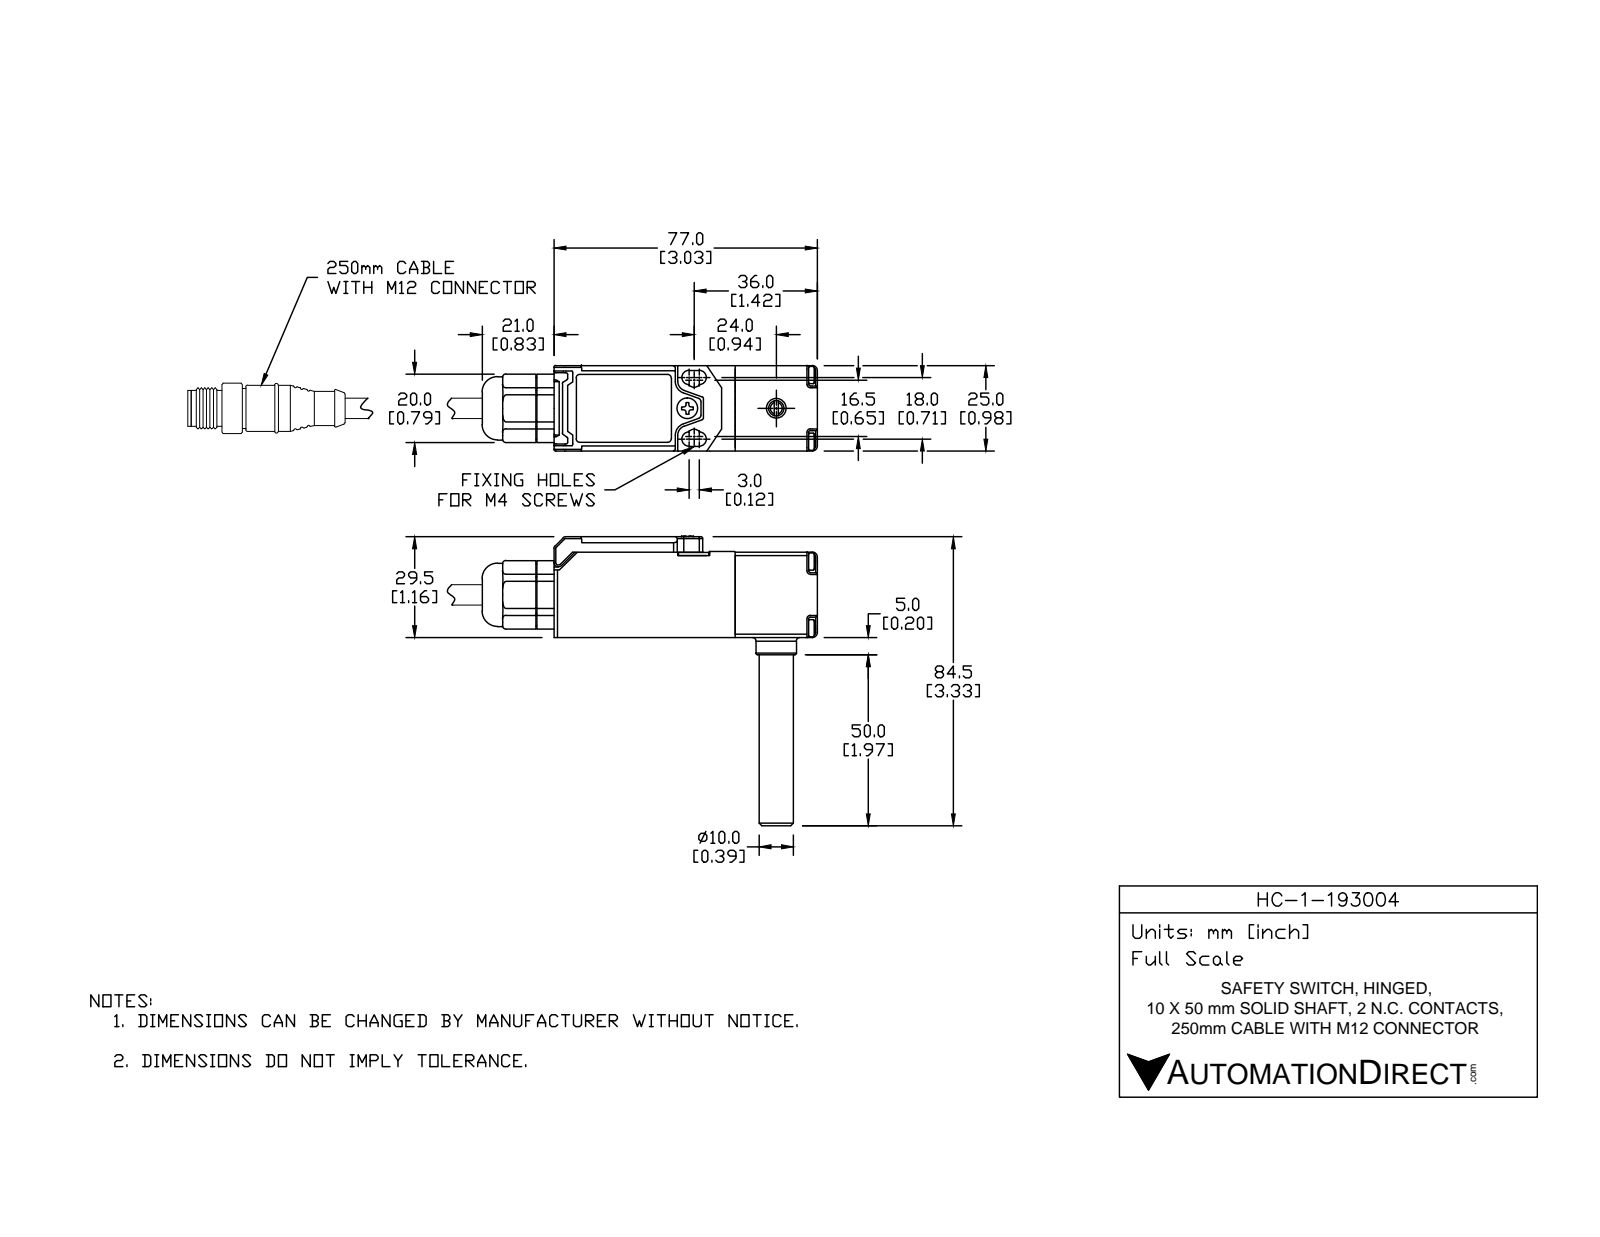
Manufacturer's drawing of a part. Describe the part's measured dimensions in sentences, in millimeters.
The part is named "HC-1-193004". Its 3-D file was written by "SolidWorks 2014 (AUTOMOTIVE_DESIGN)". It is 14 solids with 1702 faces: 700 planar, 601 cylindrical and 401 other. Overall it measures 84.7 by 80.5 by 25 millimeters. Its volume is 29 300 cubic millimeters and its surface area 27 770 square millimeters. Round holes: 5 of diameter 3.2, 4 of diameter 2.4, 2 of diameter 1.5, 2 of diameter 1.6, 2 of diameter 1.8, 2 of diameter 2.2, 2 of diameter 3.6, 1 of diameter 1.4, 1 of diameter 2.1, 1 of diameter 2.5, 1 of diameter 2.6, 1 of diameter 4.7. Round bosses or shafts: 5 of diameter 2.6, 4 of diameter 5, 4 of diameter 2, 2 of diameter 3.5, 1 of diameter 18.8, 1 of diameter 13.5, 1 of diameter 10, 1 of diameter 9.8. Partial cylindrical surfaces (rounded edges, fillets, slot ends): 226 of radius 0.5, 24 of radius 0.1, 20 of radius 0.3, 20 of radius 1, 7 of radius 1.5, 6 of radius 2.1, 6 of radius 2.8, 4 of radius 0.2. The main face-to-face distances are 25, 2, 1.8, 23.2, 1, 23, 24, 21, 22.2, 29.2. The hole center spacings are 13.8, 19.5, 4.3, 4.7, 6.2, 10.5, 10.7, 10.8.
